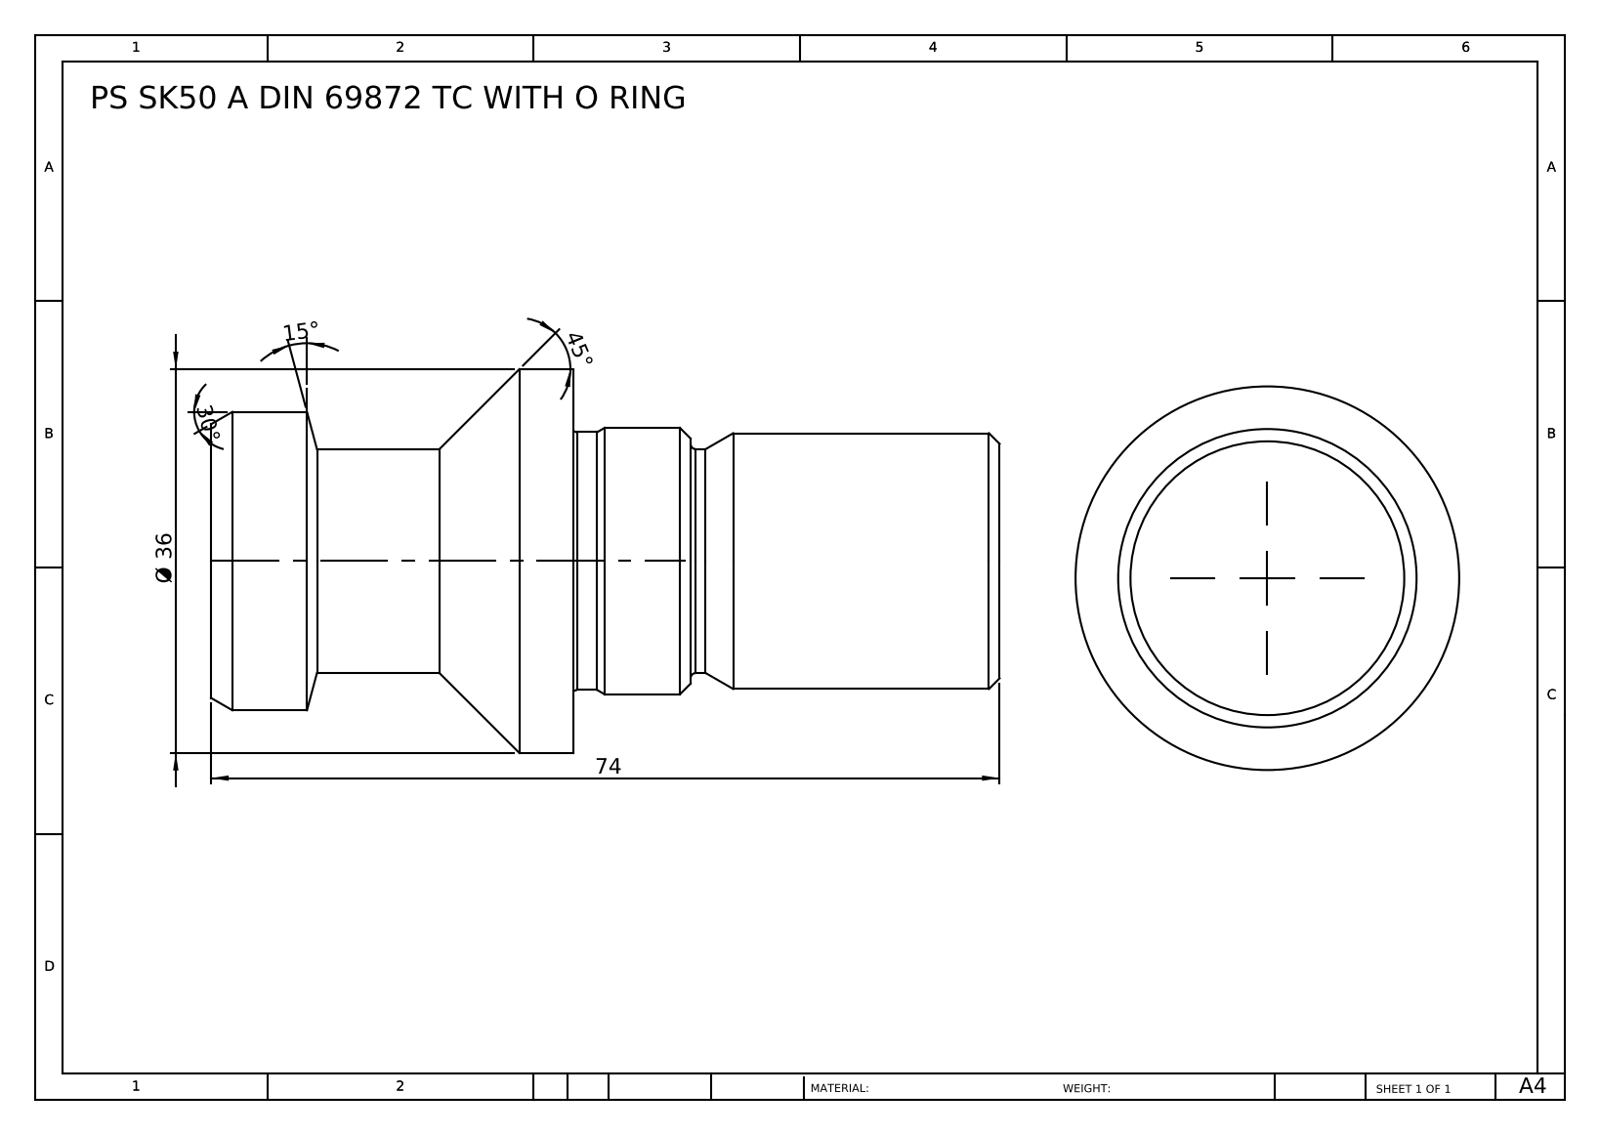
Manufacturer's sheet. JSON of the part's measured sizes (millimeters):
{"part_name": "PS SK50 A DIN 69872 TC WITH O RING", "step_written_by": "SolidWorks 2014 (CONFIG_CONTROL_DESIGN)", "units": "millimeters", "bodies": {"solids": 1, "faces": 38, "planar": 4, "cylindrical": 14, "other": 20}, "overall_size": [74, 36, 36], "volume_mm3": 38003, "surface_area_mm2": 7990, "round_bosses_or_shafts": [[36, 1], [28, 1], [25, 1], [24.2, 1], [24, 1], [21, 1]], "face_to_face_distances": [34, 40, 74, 29, 11, 45]}
